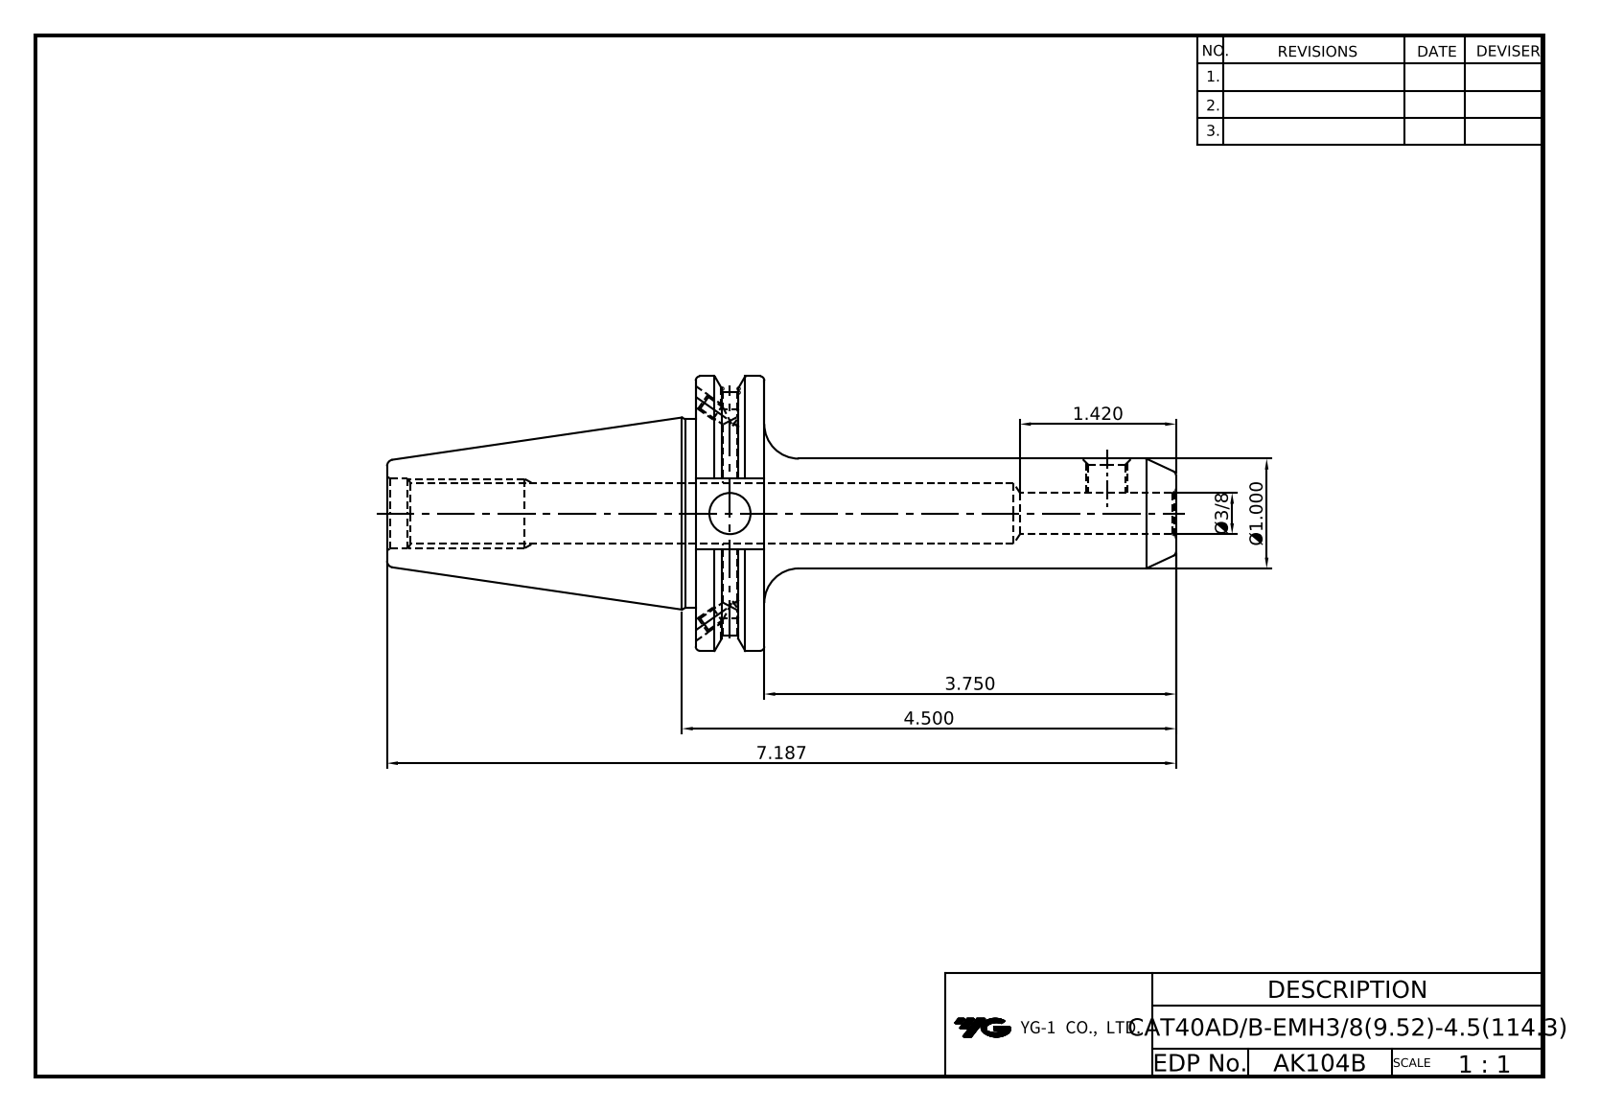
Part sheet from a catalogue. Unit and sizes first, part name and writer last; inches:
Units: inches
Overall size (bounding box): 7.187 × 2.5 × 2.405
Round holes (diameter × count): ⌀0.128 ×4, ⌀0.157 ×2, ⌀0.165 ×2, ⌀0.375 ×2, ⌀0.33 ×1, ⌀0.527 ×1, ⌀0.642 ×1
Round bosses / shafts (diameter × count): ⌀2.5 ×1, ⌀1.717 ×1, ⌀1 ×1
Partial cylindrical surfaces — rounded edges, fillets, slot ends (radius × count): R1.108 ×1
Main face-to-face distances: 0.625, 1.874, 0.645, 2.812, 3.437, 7.187, 4.375, 3.75, 3.05, 0.238
Volume: 8.377 in³ · Surface area: 49.21 in²
Bodies: 1 solid, 85 faces (35 planar, 27 cylindrical, 23 other)
Part name (STEP PRODUCT): LO-CAT40ADB-EMH9.525-114.3
STEP written by: Autodesk Inventor 2025 (AUTOMOTIVE_DESIGN)
